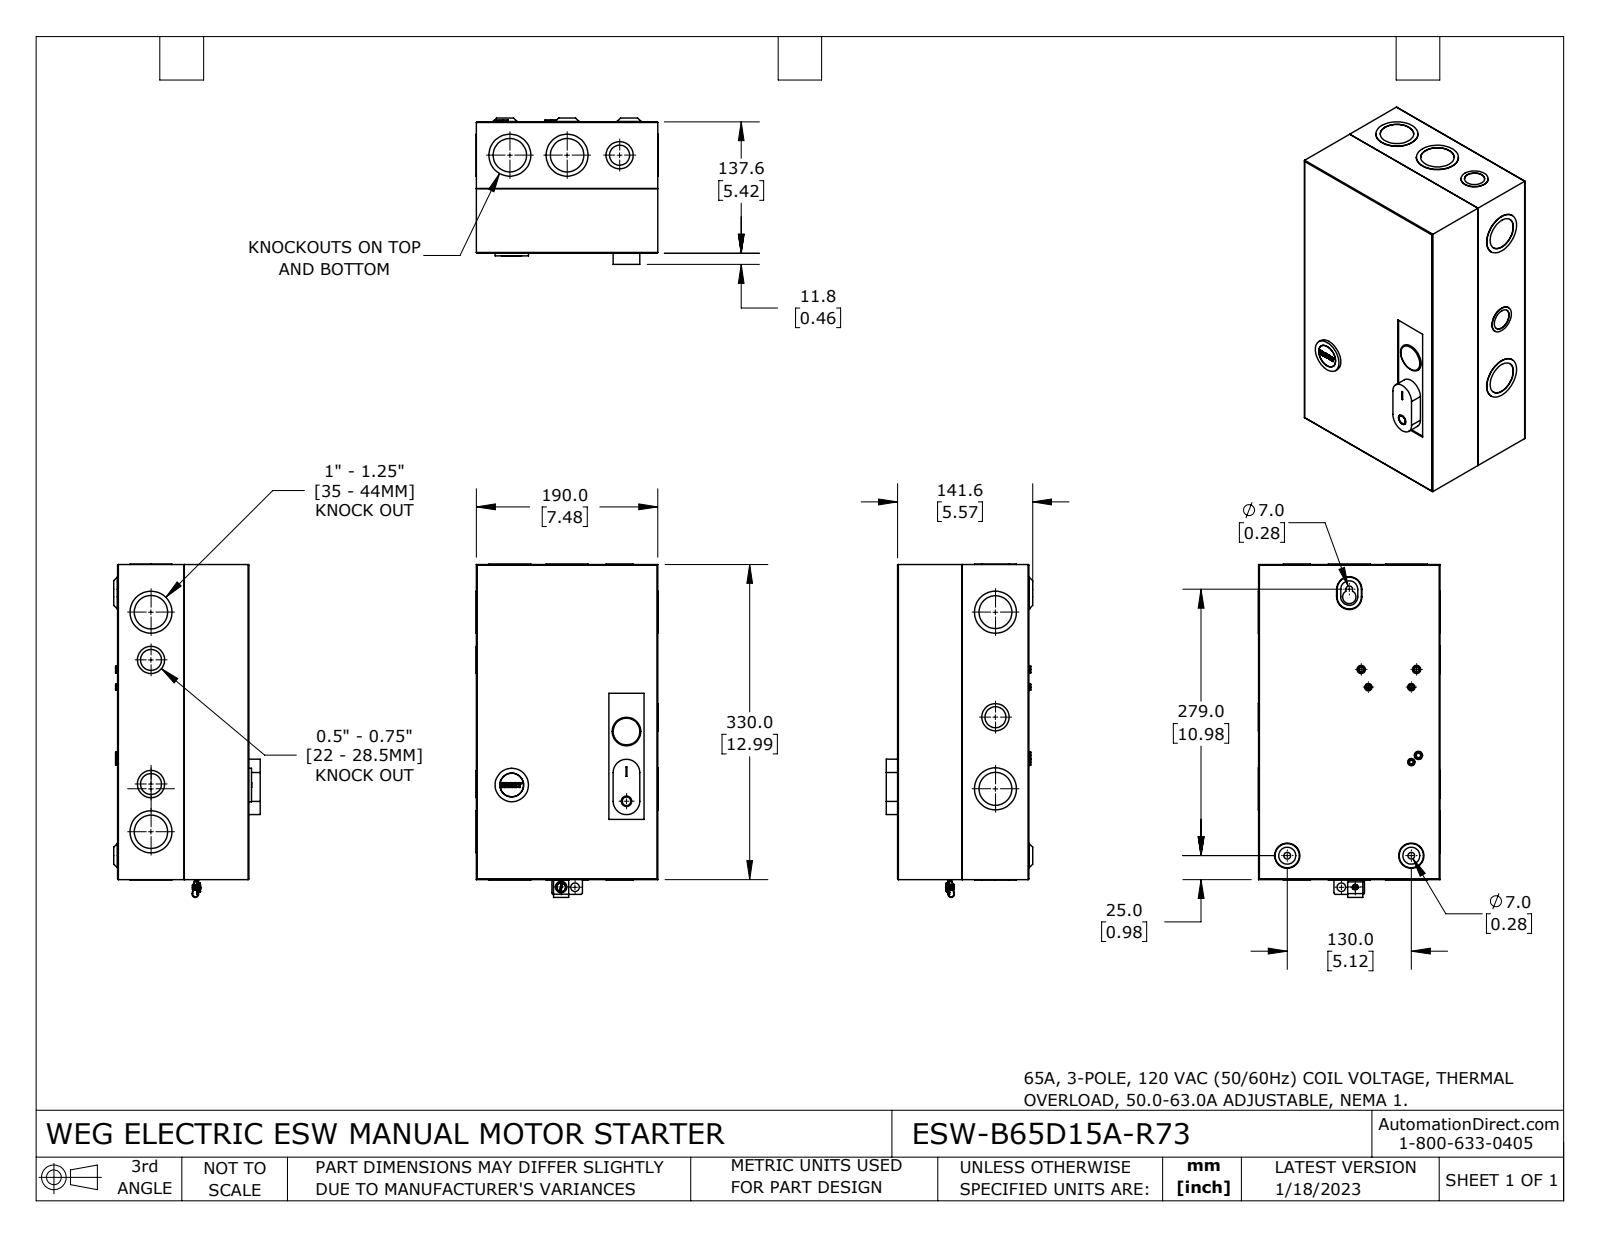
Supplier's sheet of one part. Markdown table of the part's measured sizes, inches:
| quantity | value |
| --- | --- |
| part name | ESW-B65D15A-R73 |
| STEP written by | SolidWorks 2021 (CONFIG_CONTROL_DESIGN) |
| units | inches |
| bodies | 7 solids, 435 faces (161 planar, 221 cylindrical, 53 other) |
| overall size | 13.74 × 7.504 × 6.039 |
| volume | 24.58 in³ |
| surface area | 936.7 in² |
| round holes (diameter × count) | 1.378 × 4, 0.146 × 3, 0.183 × 3, 0.276 × 2, 0.866 × 2, 0.886 × 2, 1.357 × 2, 0.256 × 1, 0.279 × 1, 0.354 × 1, 0.433 × 1, 0.469 × 1 |
| round bosses / shafts (diameter × count) | 1.732 × 4, 1.122 × 3, 0.278 × 3, 0.24 × 3, 1.734 × 2, 1.378 × 1, 1.193 × 1, 1.148 × 1 |
| partial cylindrical surfaces (radius × count) | 0.004 × 34, 0.031 × 8, 0.079 × 3, 0.138 × 3, 0.059 × 2, 0.075 × 2, 0.108 × 2, 0.122 × 2 |
| main face-to-face distances | 0.047, 5.37, 7.433, 5.323, 5.417, 12.945, 7.386, 7.48, 0.071, 12.898 |
| hole center spacings | 0.571, 1.772, 1.969, 2.283, 2.362, 5.118, 7.087, 10.972 |
